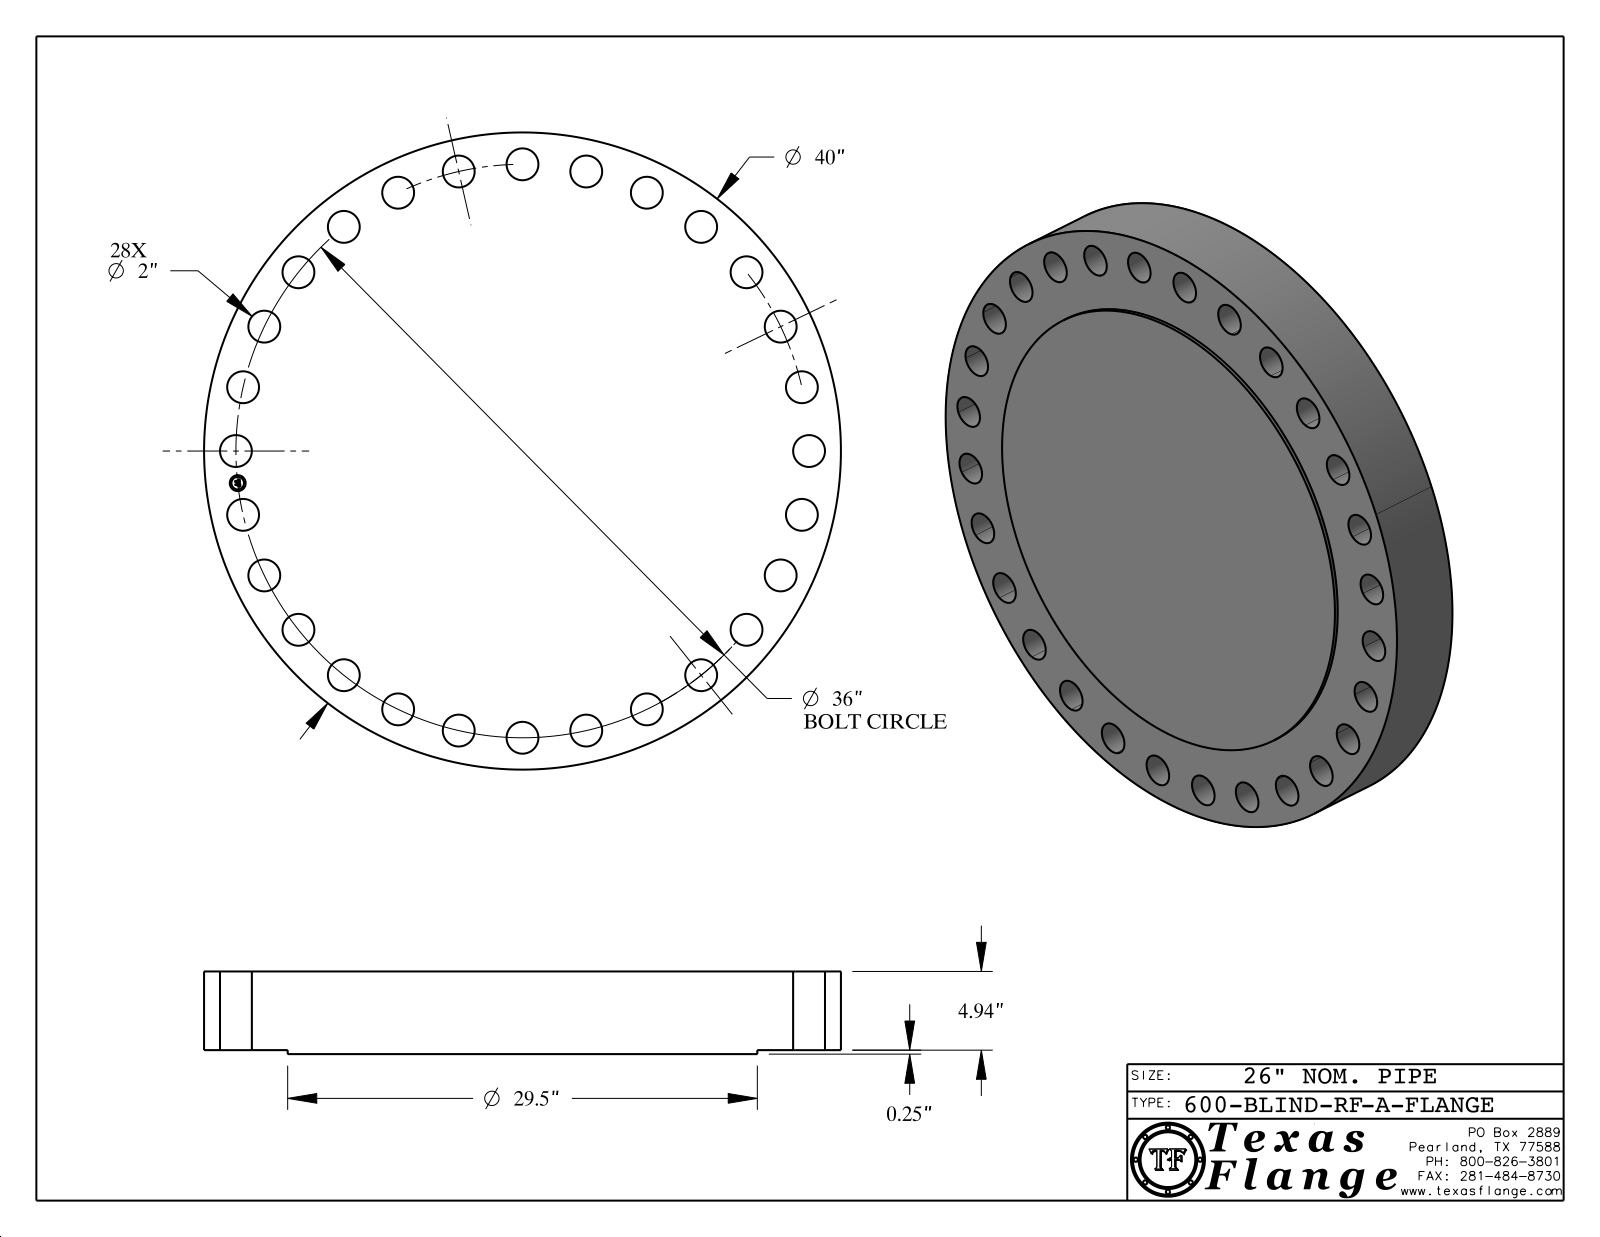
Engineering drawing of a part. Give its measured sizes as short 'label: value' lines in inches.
name: 600-BLIND-RF, Series A
written by: CATIA V5 STEP AP214 (AUTOMOTIVE_DESIGN)
unit: in
bodies: 1 solid, 448 faces (368 planar, 80 cylindrical, 0 other)
size: 40 × 40 × 5.19
volume: 5 944 in³; area: 3 851 in²
holes: 28× ⌀2, 1× ⌀1
bosses: 8× ⌀0.061, 1× ⌀40, 1× ⌀29.5, 1× ⌀0.788
face distances: 5.19, 0.25, 4.94, 0.015, 5.175, 4.925, 0.298, 0.293, 0.054, 0.193
hole spacings: 19.153, 4.031, 8.011, 11.89, 15.62, 22.446, 25.456, 32.435
